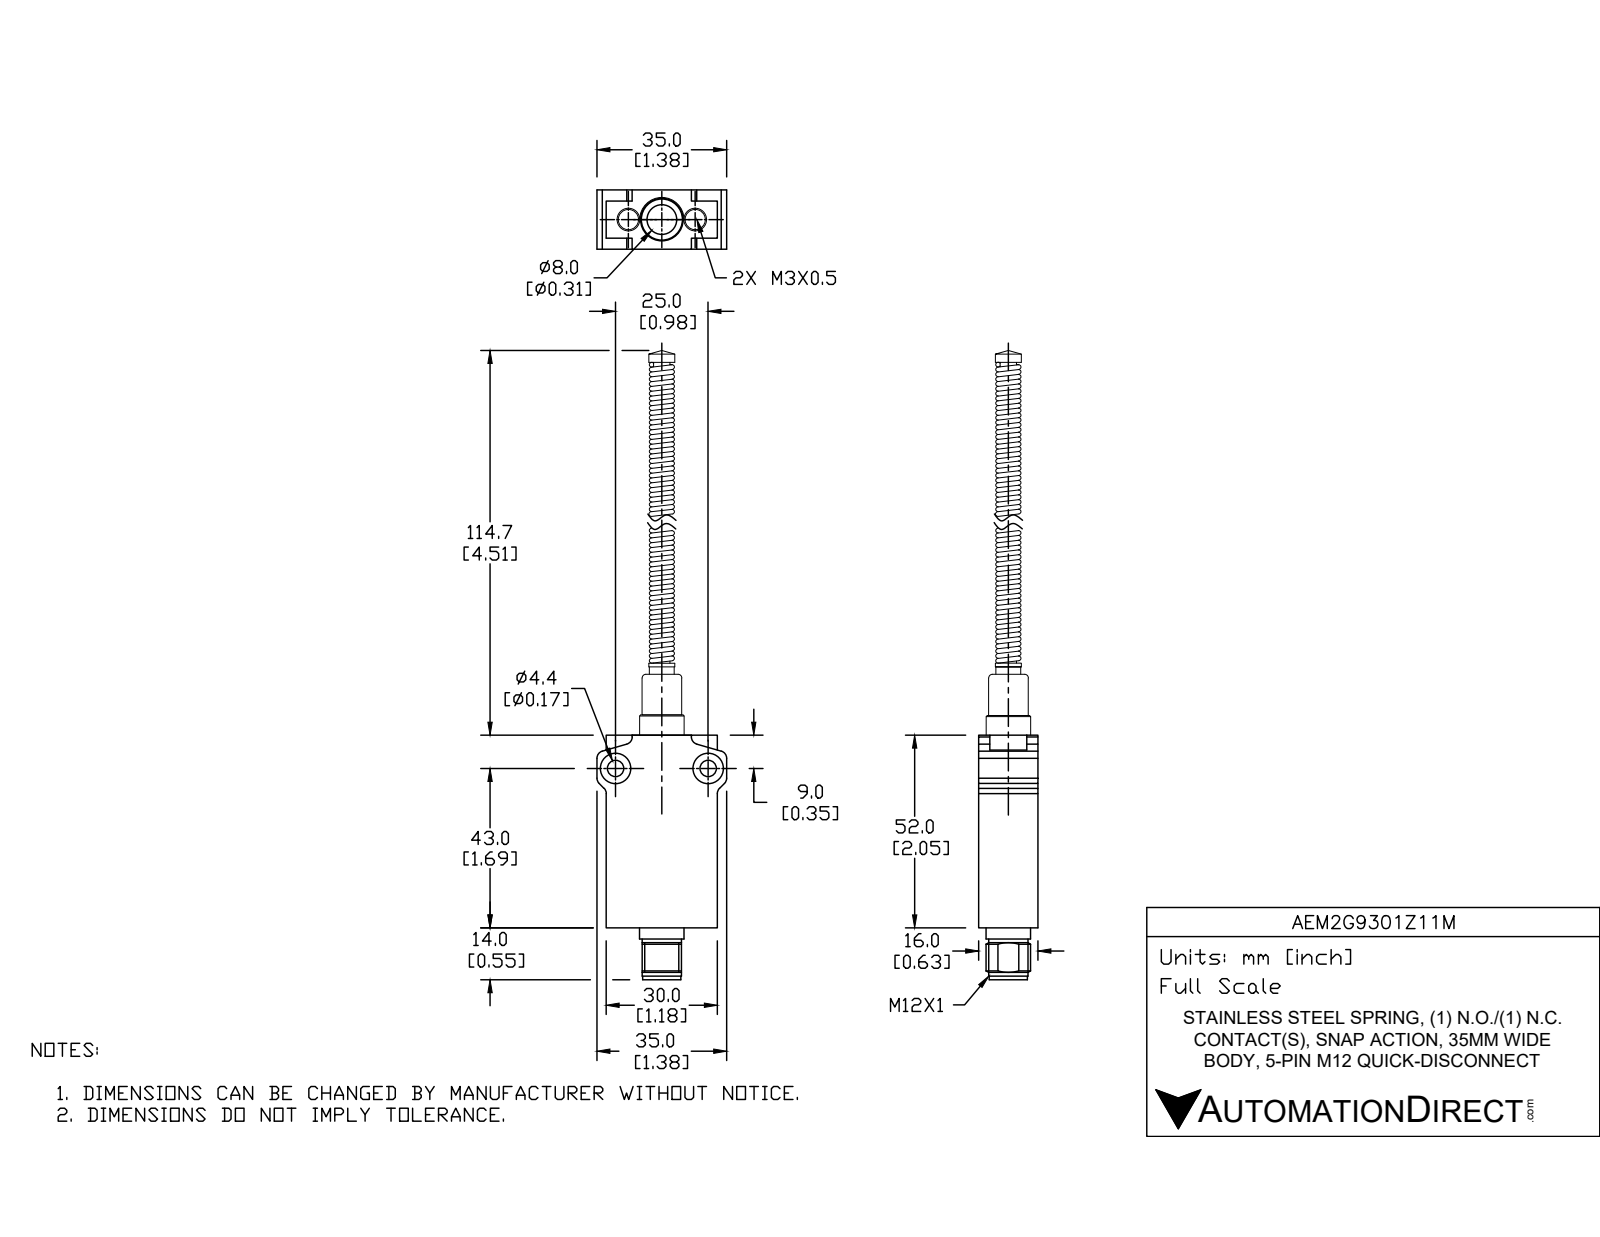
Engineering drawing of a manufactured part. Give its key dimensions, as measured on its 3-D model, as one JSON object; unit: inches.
{"part_name": "AEM2G9301Z11M", "step_written_by": "SolidWorks 2017 (AUTOMOTIVE_DESIGN)", "units": "inches", "bodies": {"solids": 4, "faces": 682, "planar": 55, "cylindrical": 68, "other": 559}, "overall_size": [6.969, 1.378, 0.63], "volume_in3": 1.872, "surface_area_in2": 17.76, "round_holes": [[0.118, 2], [0.173, 2], [0.323, 2], [0.512, 1]], "round_bosses_or_shafts": [[0.472, 1], [0.433, 1], [0.417, 1], [0.406, 1], [0.276, 1], [0.197, 1]], "partial_cylinders_radius": [[0.079, 8]], "face_to_face_distances": [0.63, 1.181, 2.047, 1.858, 0.189, 0.472, 0.098, 1.28, 0.157, 0.118], "hole_center_spacings": [0.374, 0.748, 0.984]}
